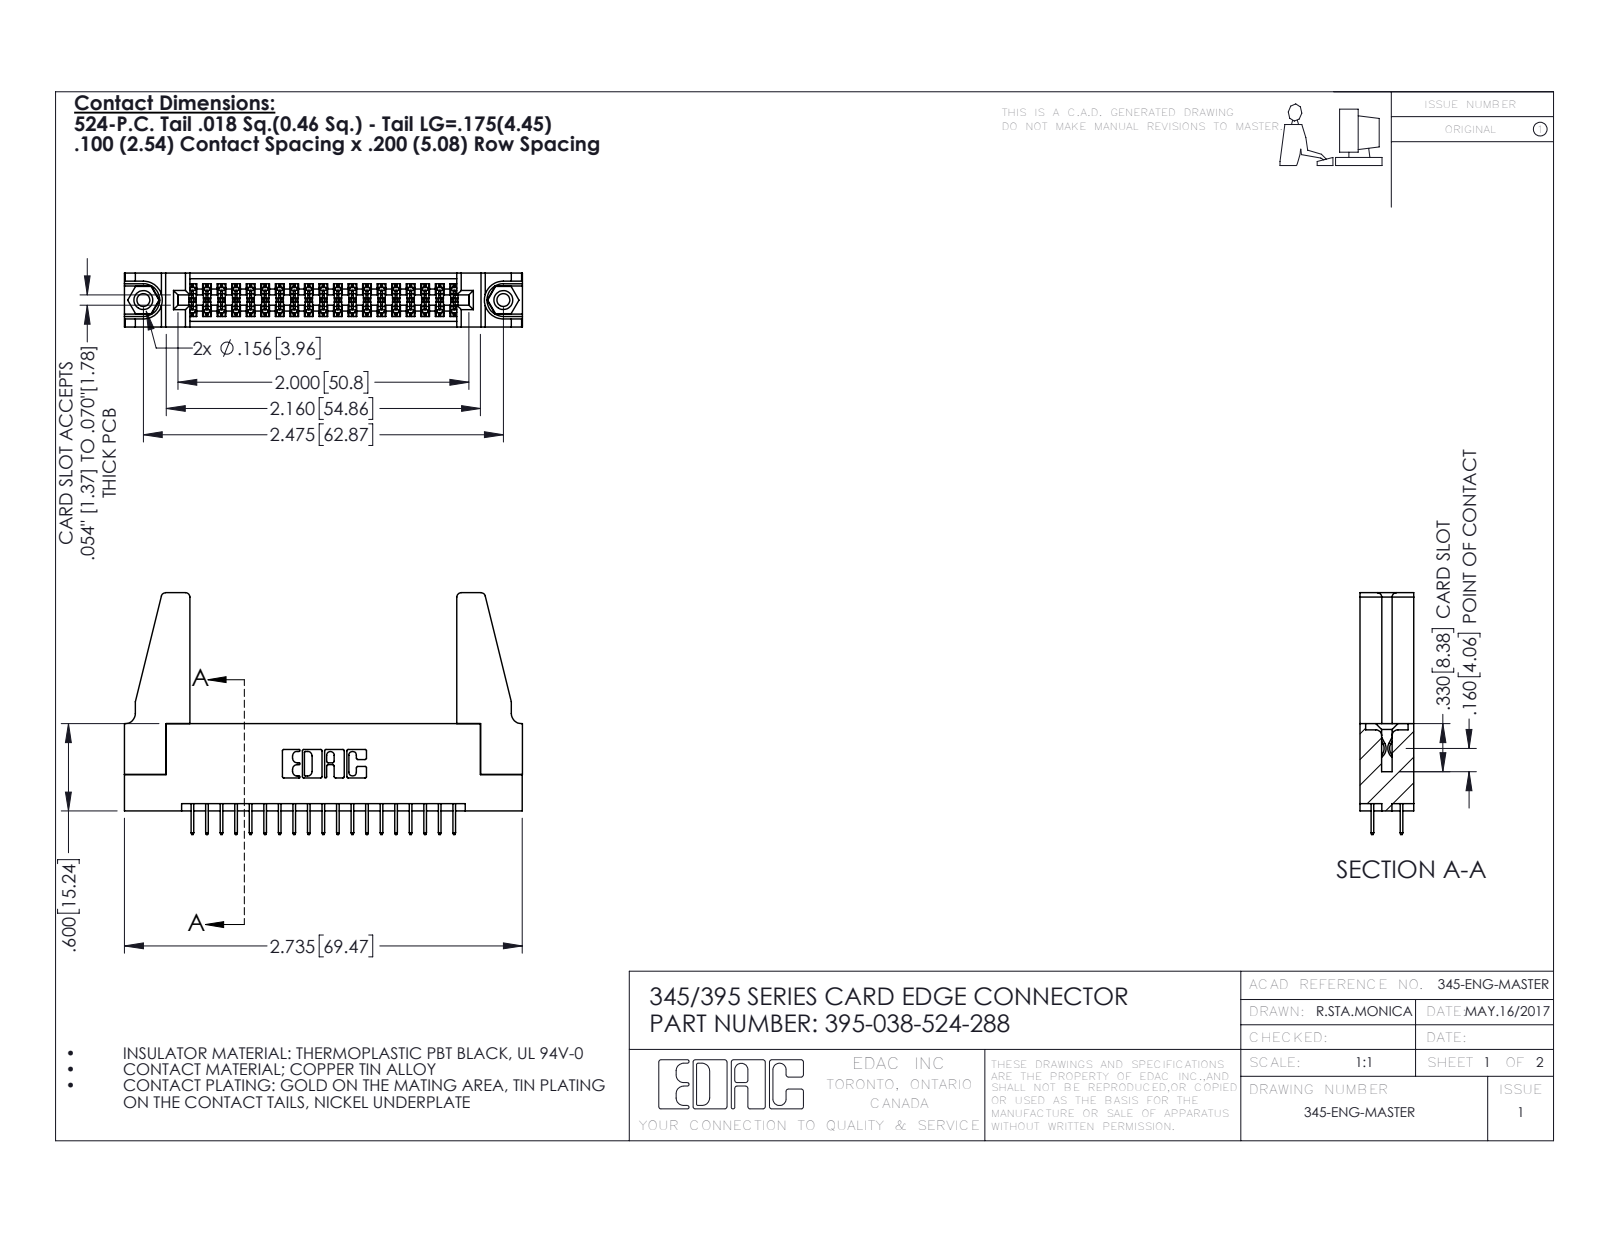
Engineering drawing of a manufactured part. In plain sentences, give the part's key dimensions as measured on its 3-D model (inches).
The part is named "395-038-524-288; 345-250-001_345-250-001-102; 345 Part_Flush Mounting Lugs - 0.156 Dia-TH; 345-292-001_345-293-124 (+1 more)". Its 3-D file was written by "SolidWorks 2016 (CONFIG_CONTROL_DESIGN)". It is 43 solids with 2302 faces: 1634 planar, 652 cylindrical and 16 other. Overall it measures 2.736 by 1.662 by 0.37 inches. Its volume is 0.594 cubic inches and its surface area 18.76 square inches. Round holes: 2 of diameter 0.089, 2 of diameter 0.125, 2 of diameter 0.156, 1 of diameter 0.064. Round bosses or shafts: 2 of diameter 0.155. Partial cylindrical surfaces (rounded edges, fillets, slot ends): 57 of radius 0.006, 22 of radius 0.01, 8 of radius 0.03, 6 of radius 0.007, 6 of radius 0.031, 3 of radius 0.026, 2 of radius 0.014, 2 of radius 0.019. The main face-to-face distances are 0.37, 0.072, 0.298, 0.2, 0.098, 0.272, 0.025, 0.225, 0.072, 0.148. The hole center spacings are 0.27, 2.241, 2.475.
